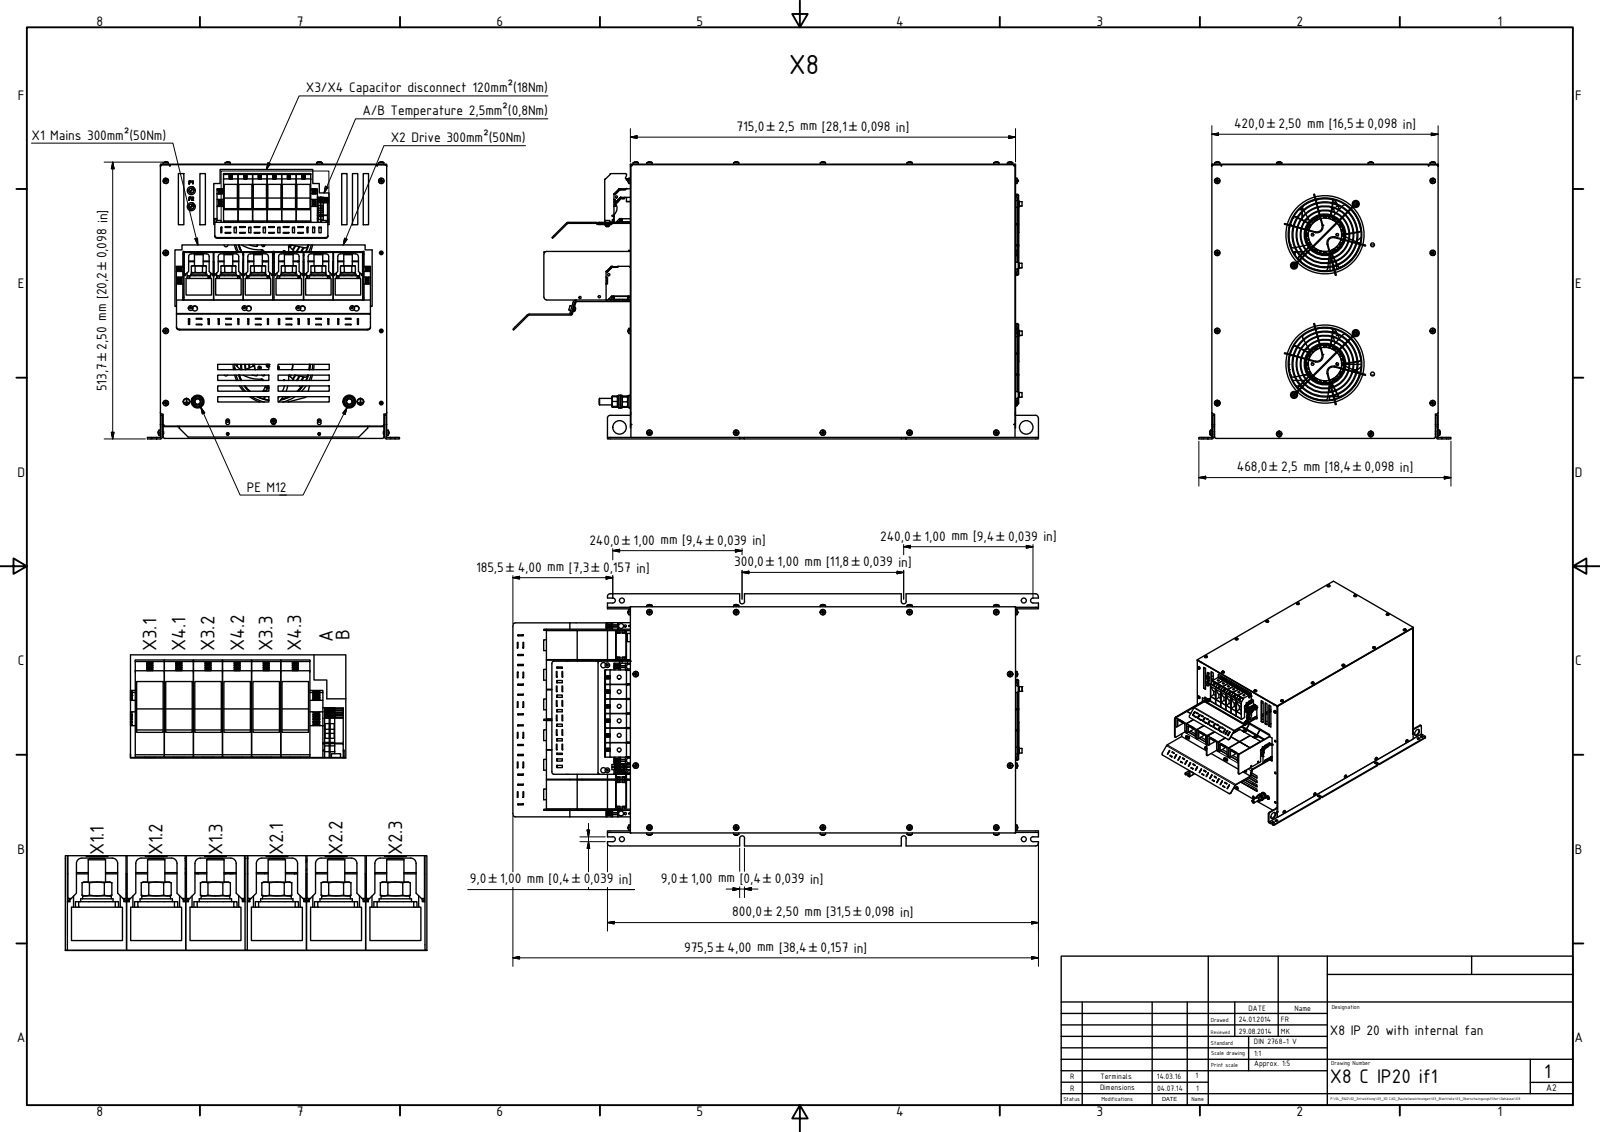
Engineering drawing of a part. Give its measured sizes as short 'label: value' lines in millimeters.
name: 10100531 Seitenwand X8-A1; 10100530 Lüfterblech X8-A1; 10100529 Anschlussblech X8-A1; DIN 7985 (Z) - M5x6-Z (+8 more)
written by: Autodesk Inventor 2015 (AUTOMOTIVE_DESIGN)
unit: mm
bodies: 151 solids, 10431 faces (6516 planar, 2318 cylindrical, 1597 other)
size: 955.04 × 515.28 × 468.01
volume: 6 646 000 mm³; area: 5 421 000 mm²
holes: 38× ⌀6.5, 36× ⌀4.13, 28× ⌀7, 20× ⌀3.24, 17× ⌀4, 10× ⌀6, 9× ⌀5, 8× ⌀4.25, 6× ⌀10, 4× ⌀3.95, 4× ⌀5.3, 4× ⌀5.4
bosses: 41× ⌀5, 36× ⌀4.6, 16× ⌀1.4, 14× ⌀16, 13× ⌀8.5, 12× ⌀30, 12× ⌀26.7, 12× ⌀4.95
rounds: 162× R1, 154× R0.83, 116× R0.15, 111× R0.1, 94× R2, 85× R0.5, 64× R0.31, 58× R0.2
face distances: 1, 419, 418, 420, 3, 714, 2, 483, 484, 486
hole spacings: 161, 36.03, 118.01, 322, 21, 483, 82, 154
